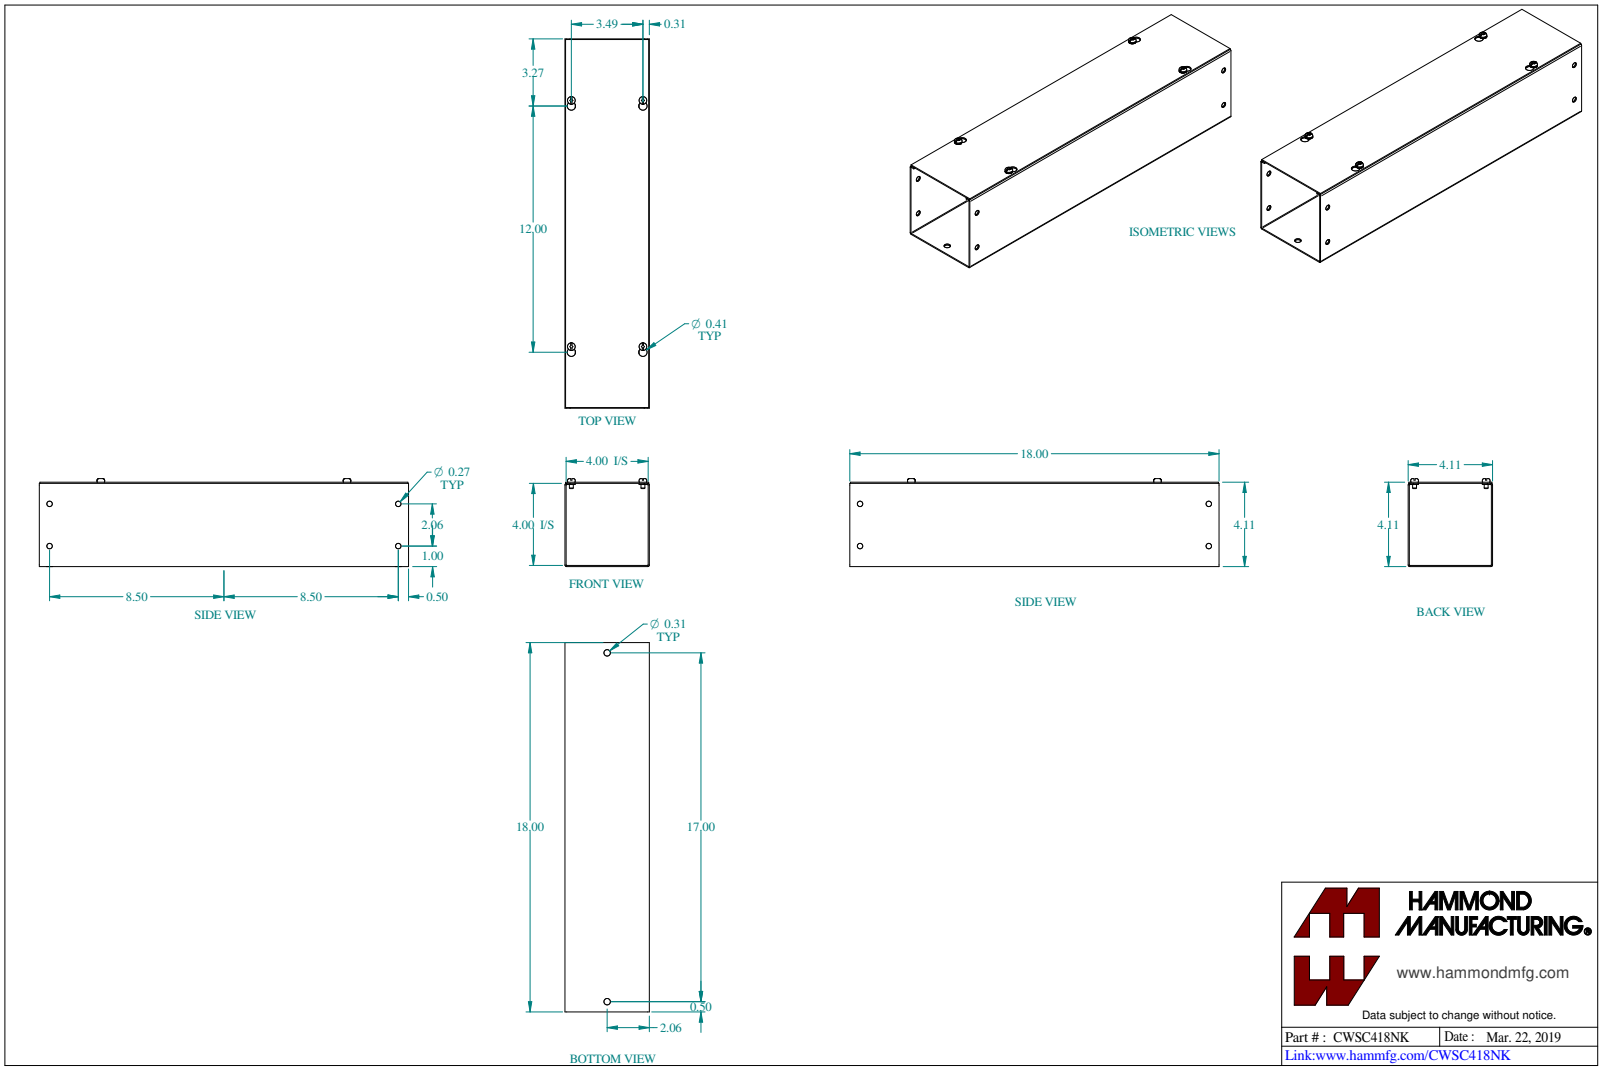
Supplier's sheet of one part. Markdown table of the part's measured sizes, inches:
| quantity | value |
| --- | --- |
| part name | CWSC418NK |
| STEP written by | SolidWorks 2023 (CONFIG_CONTROL_DESIGN) |
| units | inches |
| bodies | 6 solids, 180 faces (88 planar, 68 cylindrical, 24 other) |
| overall size | 18 × 4.289 × 4.114 |
| volume | 17.34 in³ |
| surface area | 614.3 in² |
| round holes (diameter × count) | 0.177 × 4, 0.266 × 4, 0.313 × 2 |
| round bosses / shafts (diameter × count) | 0.375 × 4, 0.19 × 4 |
| partial cylindrical surfaces (radius × count) | 0.029 × 4, 0.086 × 4, 0.125 × 4, 0.203 × 4 |
| main face-to-face distances | 0.057, 4.057, 4, 4.114, 3.943, 0.114, 0.031, 4.083, 0.026, 4.026 |
| hole center spacings | 14.605, 17, 2.057, 3.048, 3.049, 3.489, 12, 12.497 |
